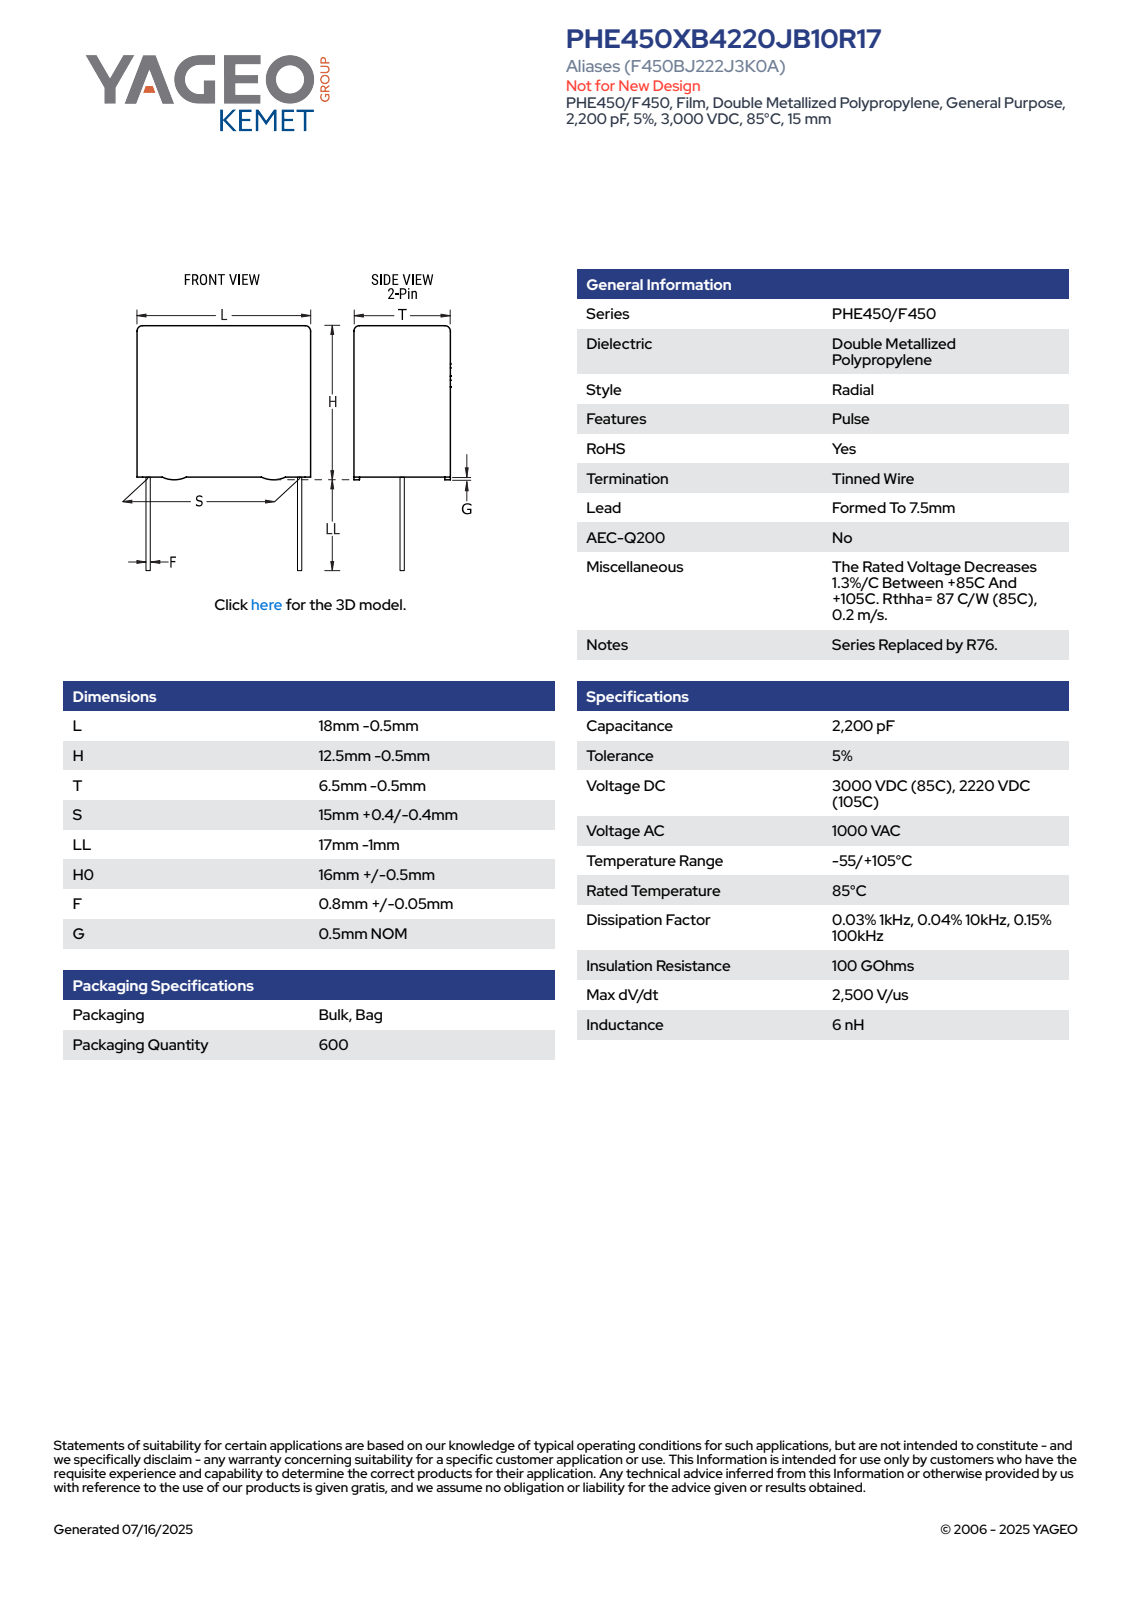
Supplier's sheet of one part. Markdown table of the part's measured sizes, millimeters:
| quantity | value |
| --- | --- |
| part name | CFR_RBG_18X12.5X6.5_L17.5H12T6S15LL16F0.85G0.5 |
| STEP written by | SolidWorks 2021 (AUTOMOTIVE_DESIGN) |
| units | millimeters |
| bodies | 4 solids, 89 faces (81 planar, 8 cylindrical, 0 other) |
| overall size | 28 × 17.5 × 6 |
| volume | 1 226 mm³ |
| surface area | 874 mm² |
| round bosses / shafts (diameter × count) | 0.85 × 2 |
| partial cylindrical surfaces (radius × count) | 0.5 × 4 |
| main face-to-face distances | 6, 11.5, 17.5, 0.34, 5.66, 0.5, 12, 5.32, 16, 16.5 |
